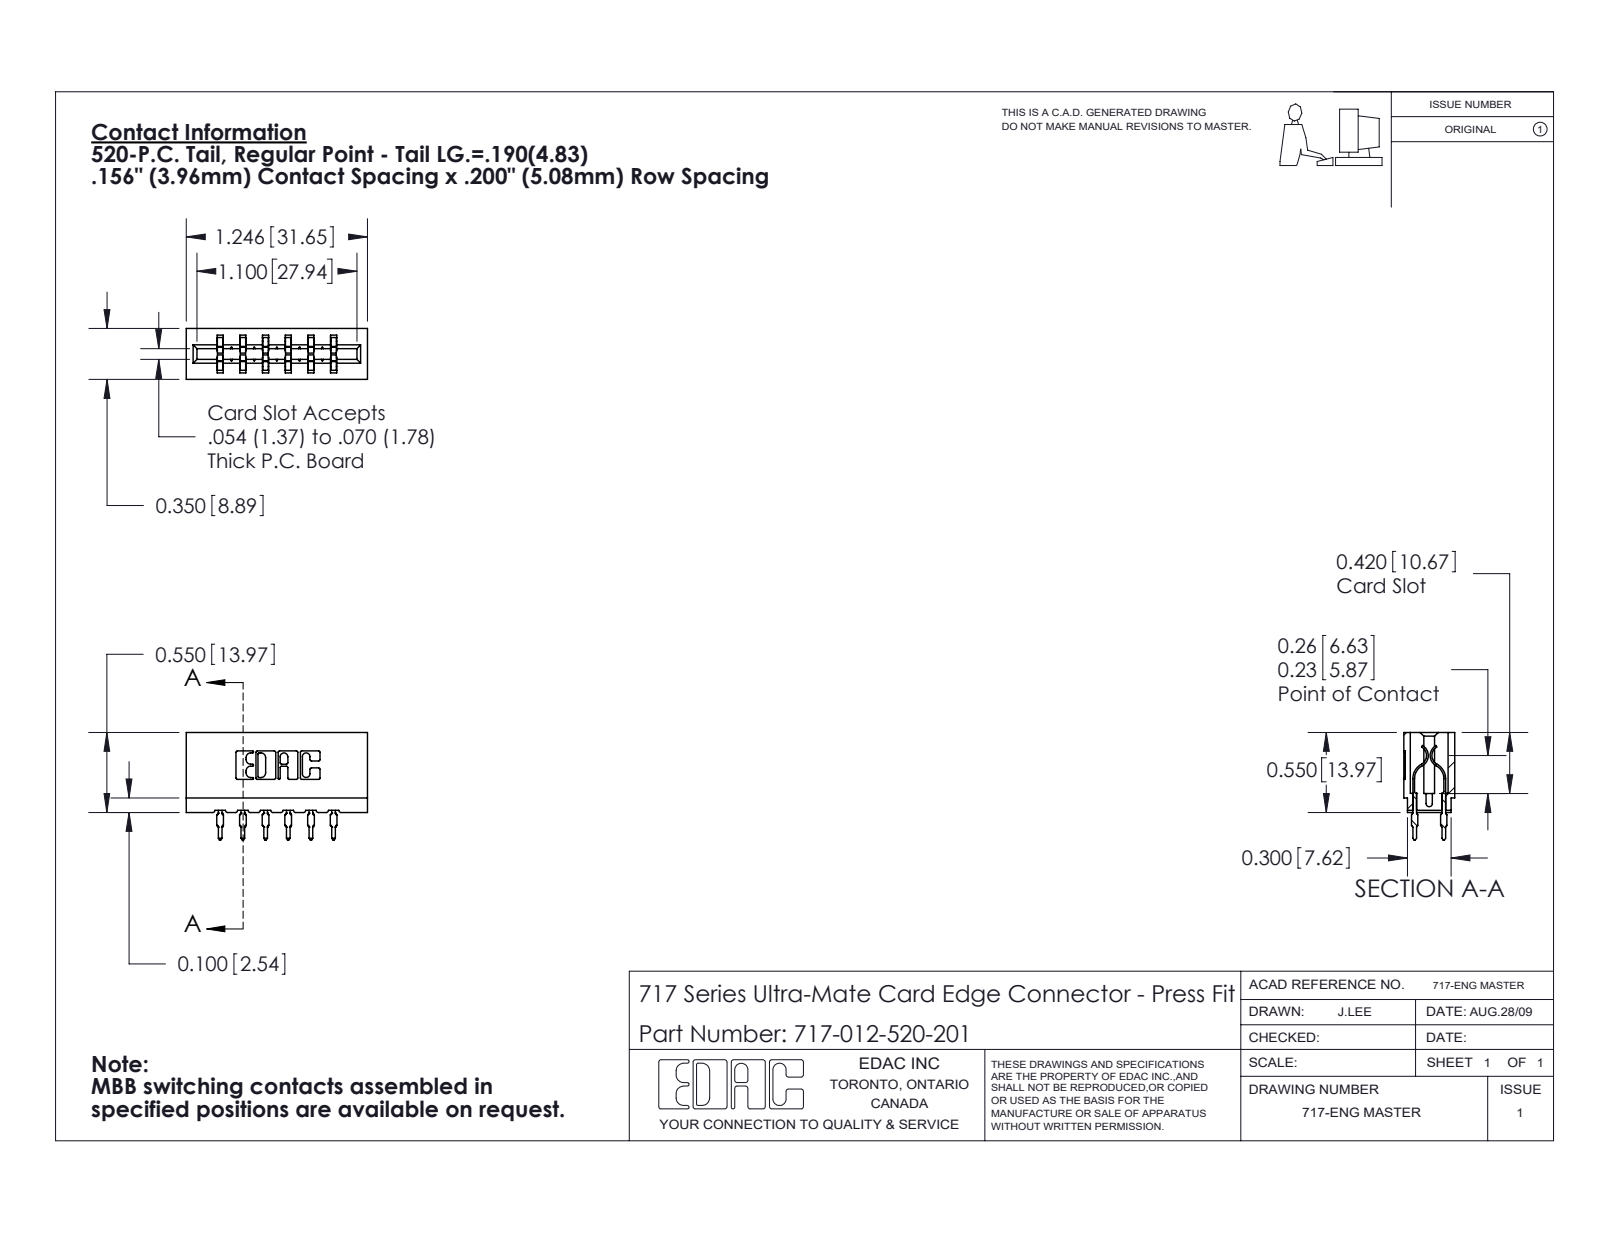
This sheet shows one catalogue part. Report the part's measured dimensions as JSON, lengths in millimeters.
{"part_name": "745-292-001_520; 717-012-520-201; 717 Part_Insulator Option - 06", "step_written_by": "SolidWorks 2020 (CONFIG_CONTROL_DESIGN)", "units": "millimeters", "bodies": {"solids": 13, "faces": 1174, "planar": 612, "cylindrical": 250, "other": 312}, "overall_size": [31.6, 18.8, 8.9], "volume_mm3": 2880, "surface_area_mm2": 3863, "partial_cylinders_radius": [[0.5, 24], [0.3, 22], [0.4, 12], [0.1, 8], [0.3, 8], [0.2, 6], [0.8, 6], [0.7, 3]], "face_to_face_distances": [5.4, 4, 3.5, 8.9, 5, 15.8, 7.9, 1.1, 7.9, 11.9]}
